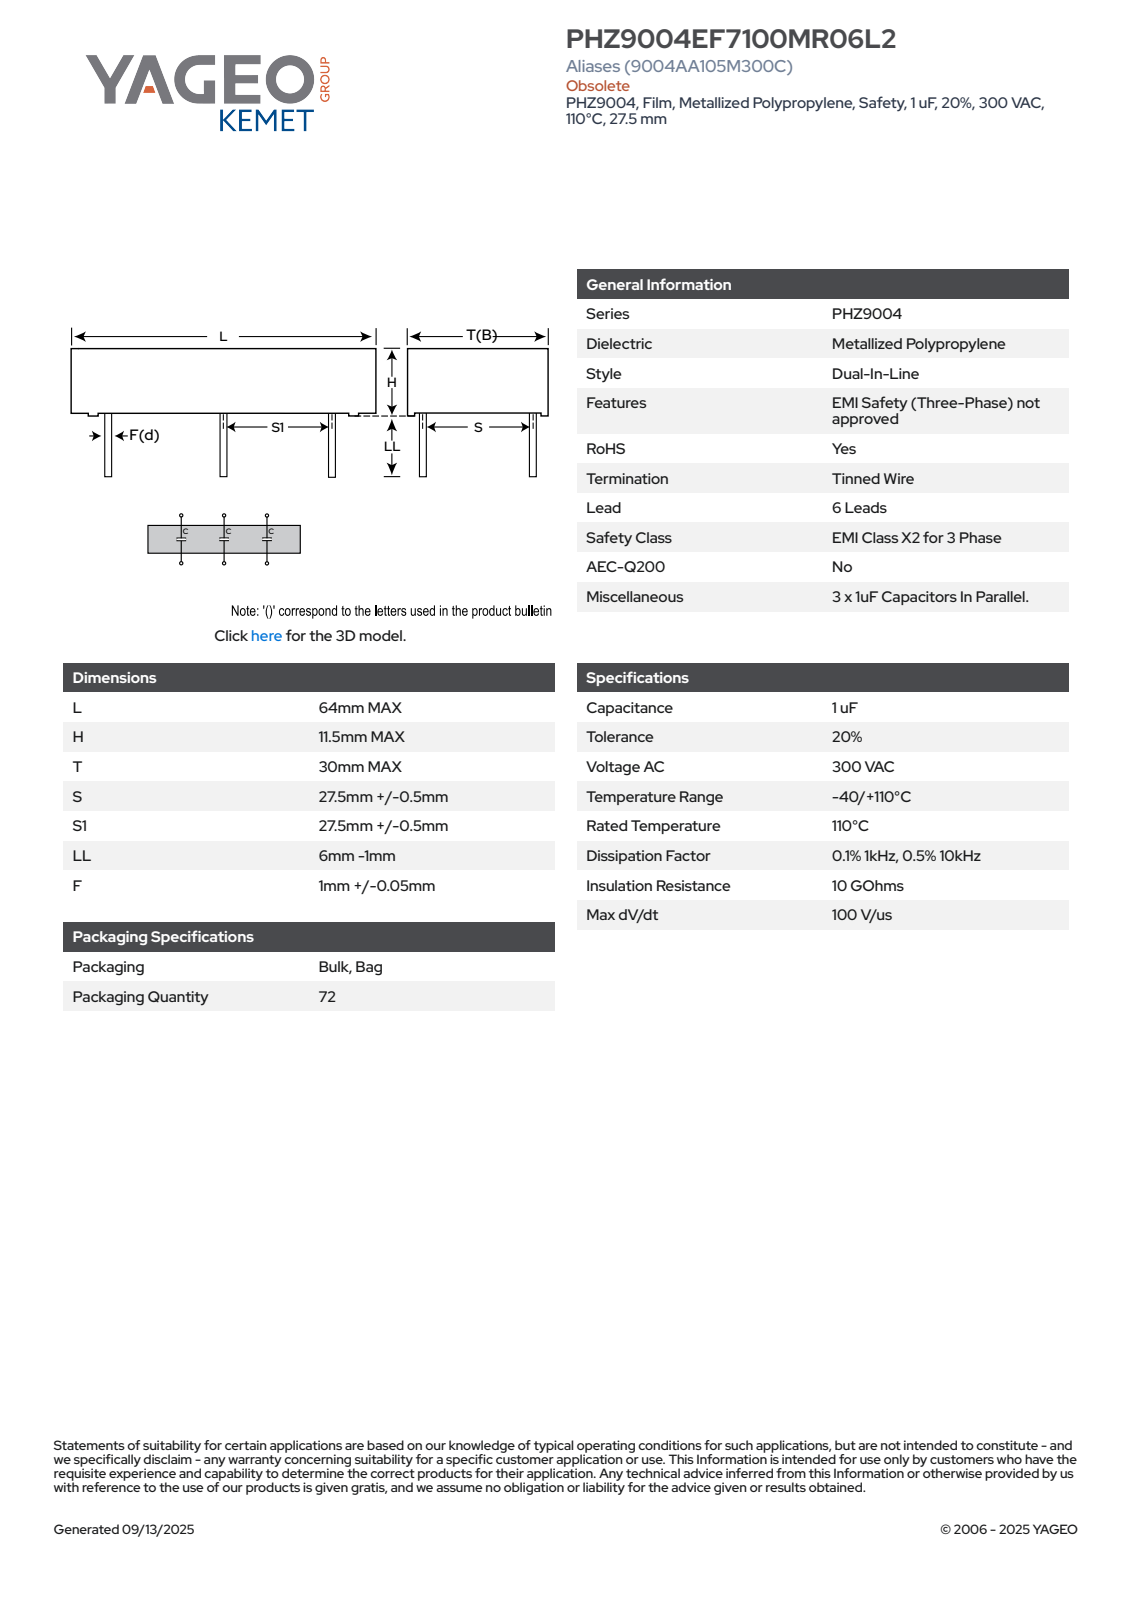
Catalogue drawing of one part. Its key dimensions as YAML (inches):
part_name: "Default"
step_written_by: "SolidWorks 2014 (AUTOMOTIVE_DESIGN)"
units: inches
bodies: {solids: 4, faces: 101, planar: 85, cylindrical: 16, other: 0}
overall_size: [2.52, 1.181, 0.65]
volume: 1.288
surface_area: 9.367
round_bosses_or_shafts:
  - {diameter: 0.041, count: 6}
partial_cylinders:
  - {radius: 0.039, count: 4}
face_to_face_distances: [0.433, 1.181, 2.52, 0.02, 0.453, 0.65, 0.197, 0.217, 0.039, 1.142]
